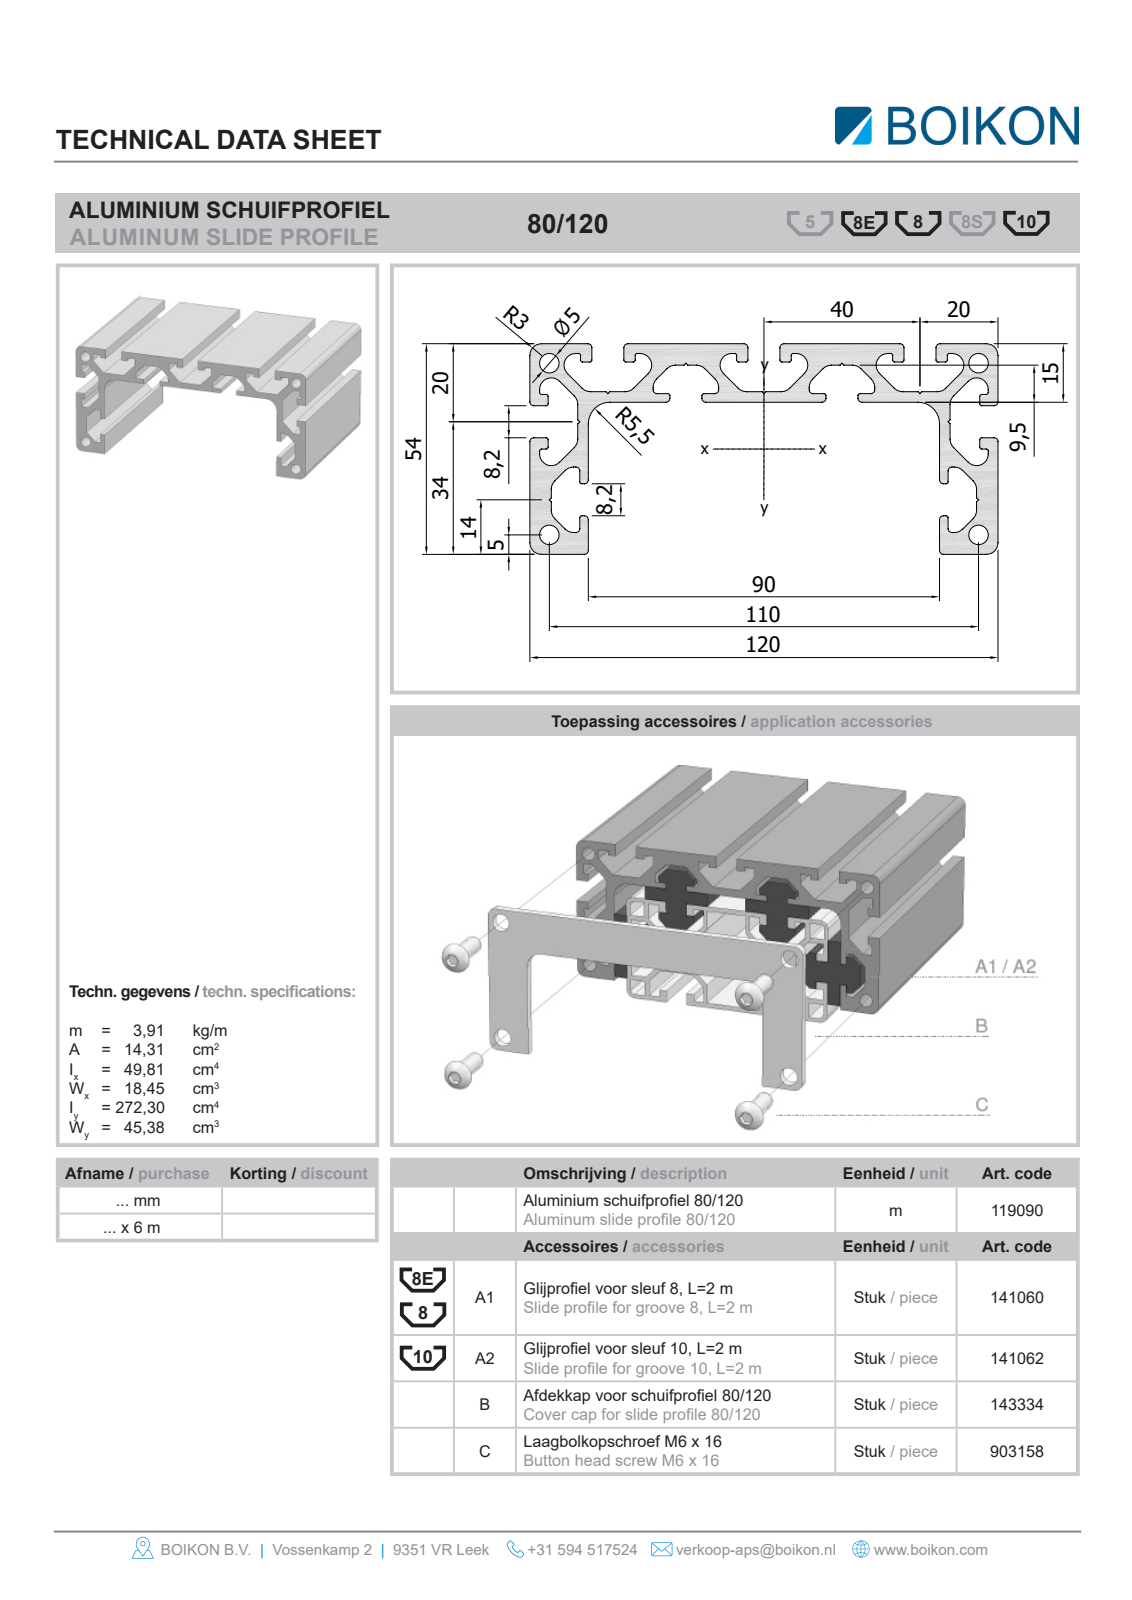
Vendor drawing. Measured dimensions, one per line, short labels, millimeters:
name: Root; 119090Alu Schuifprofiel 80/120BOIKON0
written by: HiCAD 2013 1802.4 Build 509 (AUTOMOTIVE_DESIGN)
unit: mm
bodies: 1 solid, 130 faces (120 planar, 10 cylindrical, 0 other)
size: 1000 × 120 × 54
volume: 1 491 000 mm³; area: 863 499 mm²
holes: 4× ⌀5
rounds: 4× R3, 2× R5.5
face distances: 15, 2.9, 12.1, 105, 28.28, 9.2, 120, 2.93, 9.9, 4.5
hole spacings: 44, 110, 118.47
